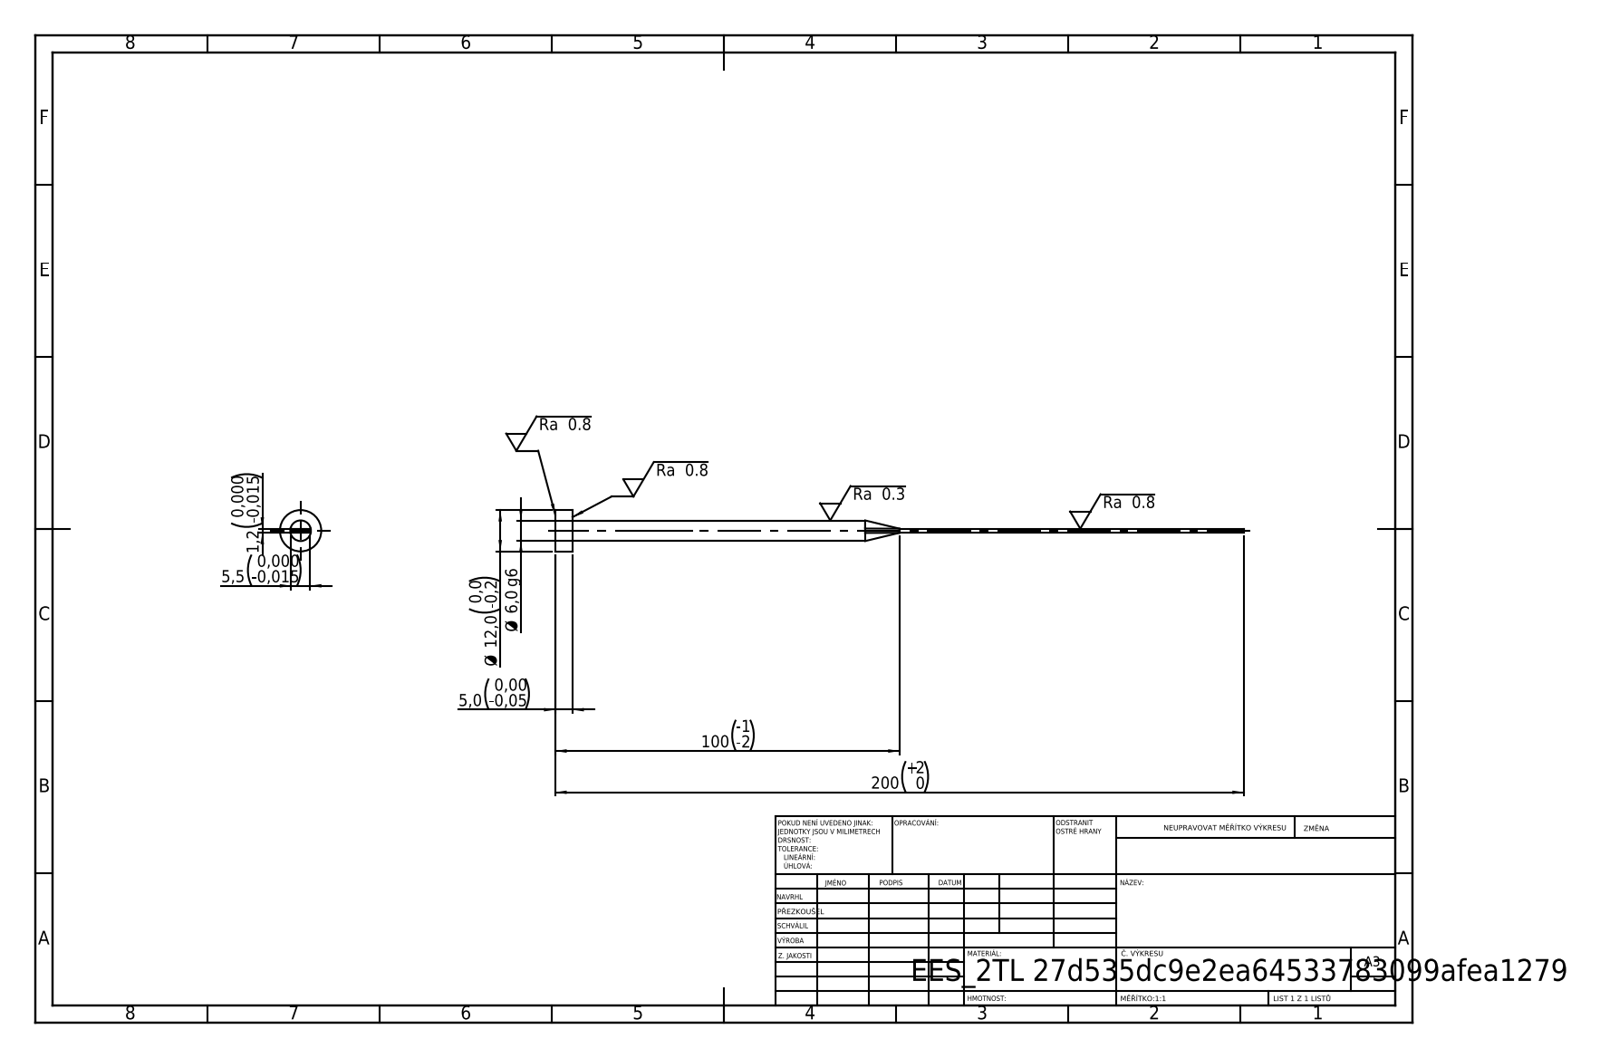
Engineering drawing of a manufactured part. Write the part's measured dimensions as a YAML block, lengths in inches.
step_written_by: "SolidWorks 2019 (CONFIG_CONTROL_DESIGN)"
units: inches
bodies: {solids: 1, faces: 15, planar: 7, cylindrical: 4, other: 4}
overall_size: [7.874, 0.472, 0.472]
volume: 0.232
surface_area: 5.413
round_bosses_or_shafts:
  - {diameter: 0.472, count: 1}
  - {diameter: 0.236, count: 1}
face_to_face_distances: [0.047, 0.217, 0.197, 7.874, 7.677]
